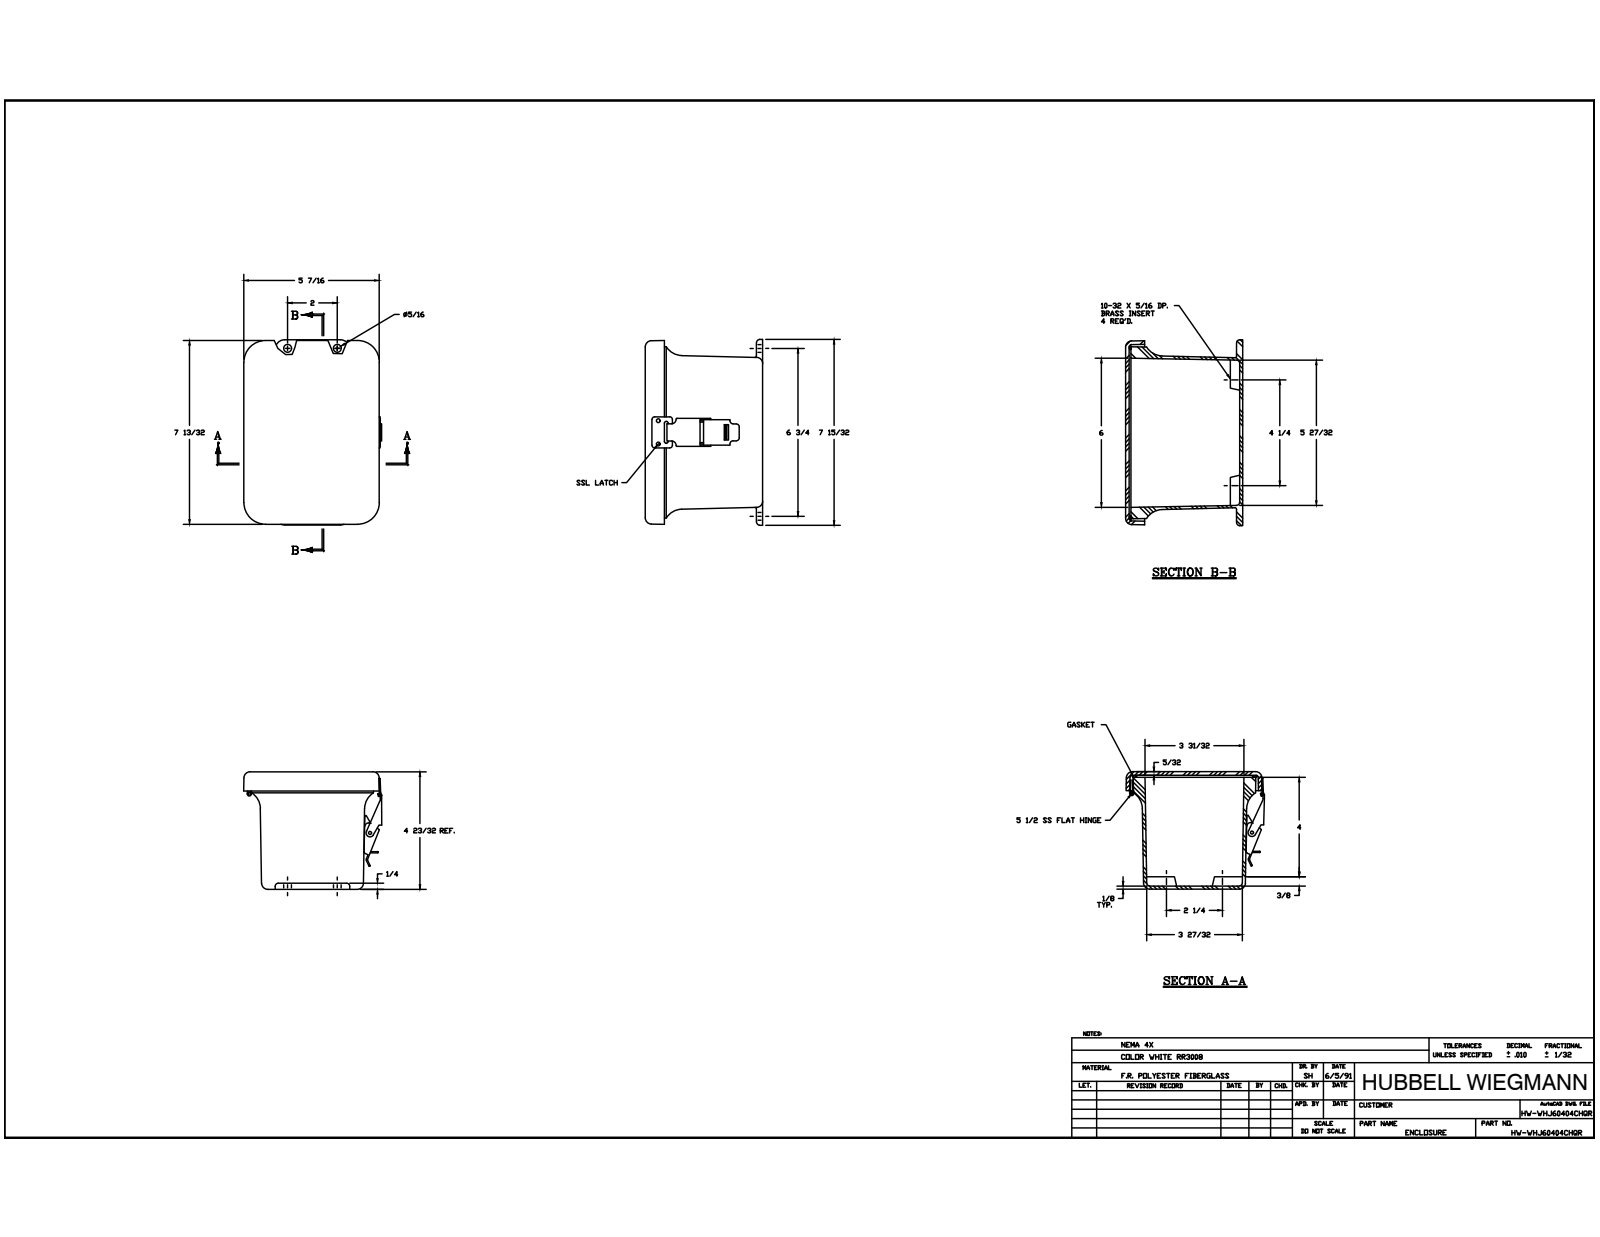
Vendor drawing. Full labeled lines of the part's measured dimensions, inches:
Part name (STEP PRODUCT): J604HL_2; RMINS45821P_19; RMINS45821P_20; RMINS45821P_21 (+8 more)
STEP written by: Autodesk Inventor 2014 (AUTOMOTIVE_DESIGN)
Units: inches
Bodies: 25 solids, 627 faces (249 planar, 254 cylindrical, 124 other)
Overall size (bounding box): 7.474 × 5.622 × 4.718
Volume: 31.6 in³ · Surface area: 407.8 in²
Round holes (diameter × count): ⌀0.14 ×11, ⌀0.131 ×5, ⌀0.152 ×5, ⌀0.104 ×4, ⌀0.156 ×4, ⌀0.218 ×4, ⌀0.13 ×2, ⌀0.135 ×2, ⌀0.085 ×1, ⌀0.375 ×1
Round bosses / shafts (diameter × count): ⌀0.125 ×9, ⌀0.25 ×5, ⌀0.27 ×4, ⌀0.3 ×1, ⌀0.17 ×1, ⌀0.155 ×1, ⌀0.12 ×1
Partial cylindrical surfaces — rounded edges, fillets, slot ends (radius × count): R0.031 ×20, R0.125 ×16, R0.015 ×12, R0.045 ×8, R0.25 ×8, R0.03 ×6, R0.022 ×5, R0.06 ×4
Main face-to-face distances: 0.145, 4.573, 4.718, 0.125, 4.448, 4.593, 4.5, 4.375, 0.073, 0.218
Hole centre spacings: 0.937, 2.5, 3.339, 0.75, 0.469, 0.5, 1.341, 1.467
